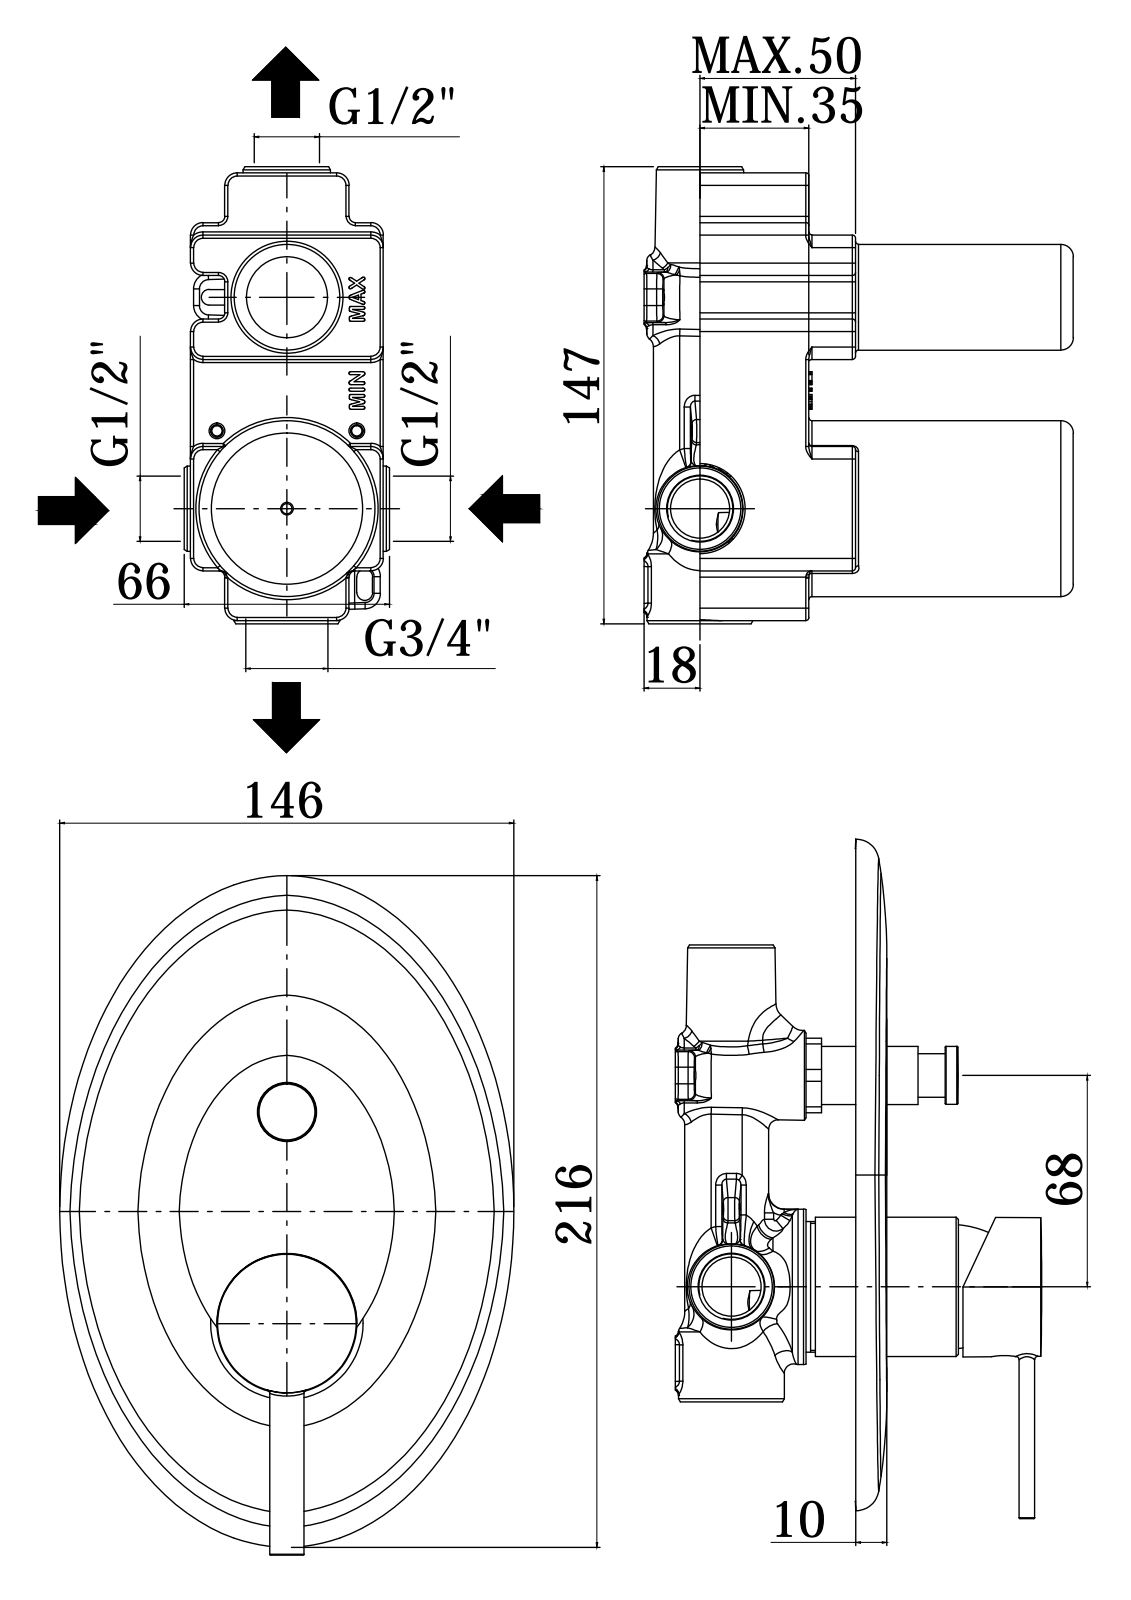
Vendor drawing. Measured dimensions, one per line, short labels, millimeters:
name: BR015CR
written by: CREO PARAMETRIC BY PTC INC, 2020044 (CONFIG_CONTROL_DESIGN)
unit: mm
bodies: 5 solids, 1081 faces (601 planar, 255 cylindrical, 225 other)
size: 216 × 146 × 61.3
volume: 117 621 mm³; area: 97 906 mm²
holes: 3× ⌀5, 3× ⌀7, 2× ⌀2, 2× ⌀4, 1× ⌀3, 1× ⌀3.3, 1× ⌀3.5, 1× ⌀10.5, 1× ⌀14.8, 1× ⌀19.2, 1× ⌀19.5, 1× ⌀19.9
bosses: 2× ⌀4.8, 1× ⌀51, 1× ⌀49, 1× ⌀44.8, 1× ⌀39, 1× ⌀35, 1× ⌀34.8, 1× ⌀32.2
rounds: 27× R0.5, 11× R0.15, 4× R0.3, 4× R1, 4× R1.25, 2× R0.8, 2× R2.75, 1× R2.5
face distances: 59, 1.5, 8.3, 50.7, 29, 2, 0.5, 9, 6.3, 20.7
hole spacings: 8.6, 13.45, 15.13, 21.93, 58.69, 73.33, 6.9, 14
